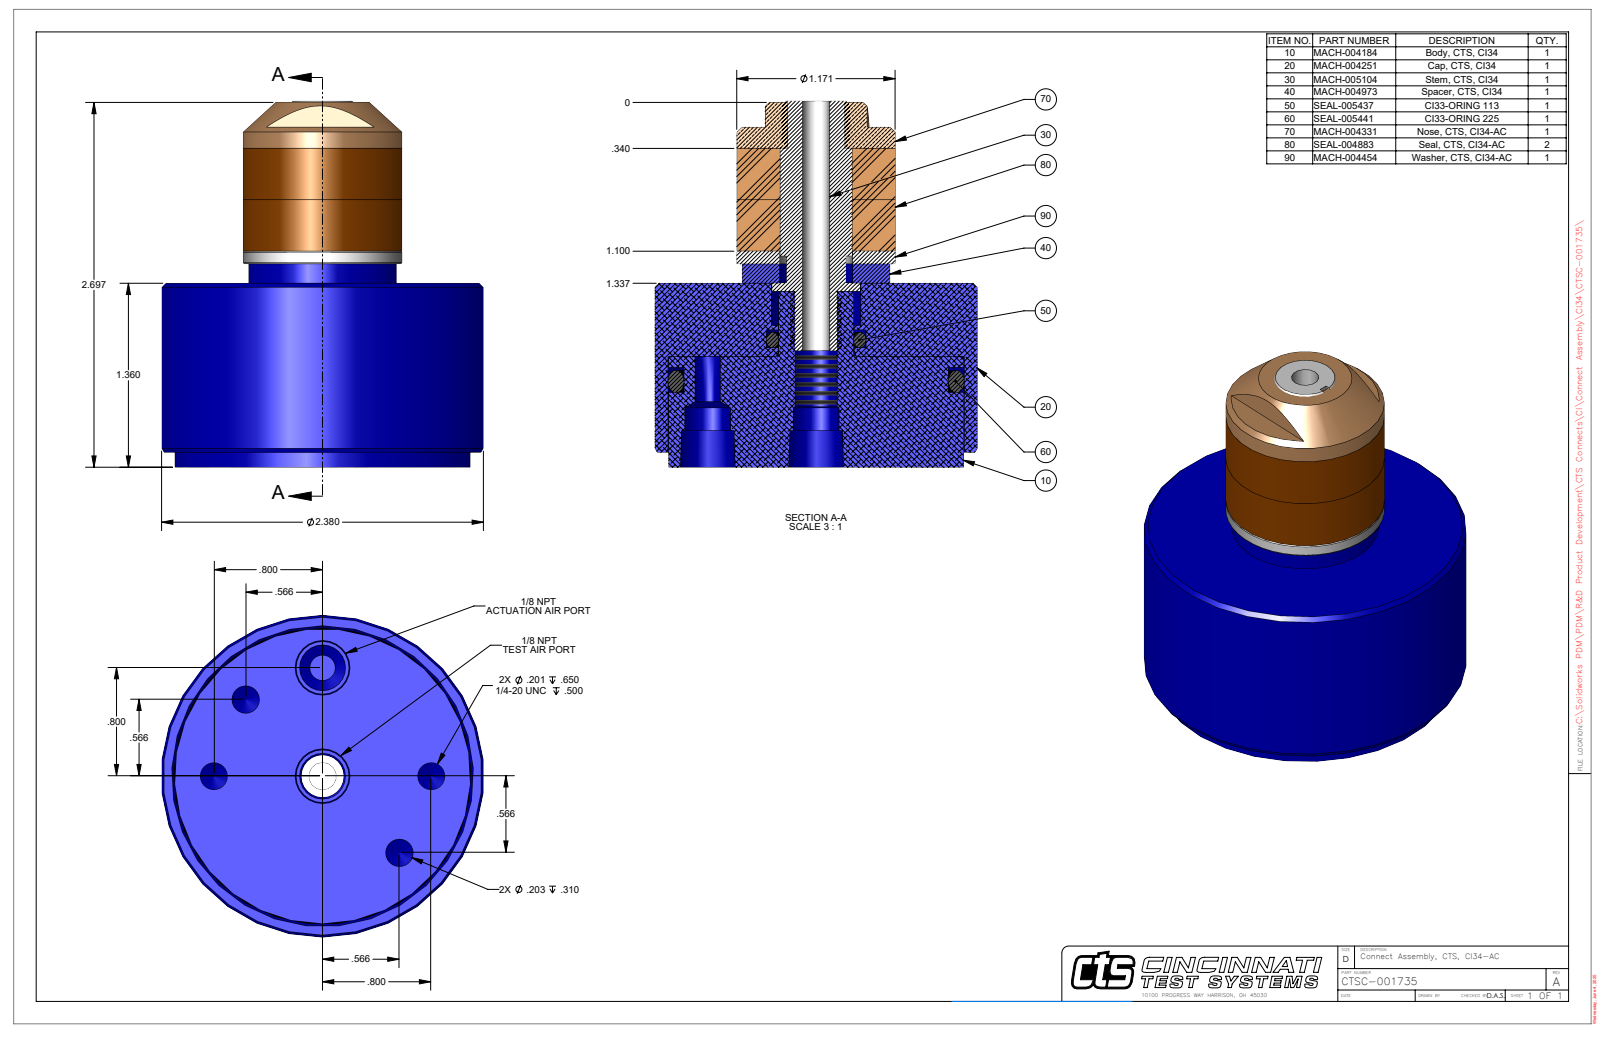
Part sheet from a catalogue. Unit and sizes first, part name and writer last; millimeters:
Units: millimetres
Overall size (bounding box): 68.7 × 60.5 × 60.5
Round holes (diameter × count): ⌀5.1 ×2, ⌀5.2 ×2, ⌀8.6 ×2, ⌀5.2 ×1, ⌀55.6 ×1
Round bosses / shafts (diameter × count): ⌀60.5 ×1, ⌀55.3 ×1, ⌀29.7 ×1, ⌀27.7 ×1
Partial cylindrical surfaces — rounded edges, fillets, slot ends (radius × count): R5.4 ×1
Main face-to-face distances: 34.5, 2.8, 31.8, 11.4, 8.6, 23.2, 68.5, 65.7, 57.1, 34
Hole centre spacings: 20.3, 15.5, 37.5, 28.7, 40.6
Volume: 115 600 mm³ · Surface area: 20 280 mm²
Bodies: 1 solid, 76 faces (22 planar, 27 cylindrical, 27 other)
Part name (STEP PRODUCT): CTSC-001735
STEP written by: SolidWorks 2023 (AUTOMOTIVE_DESIGN)
